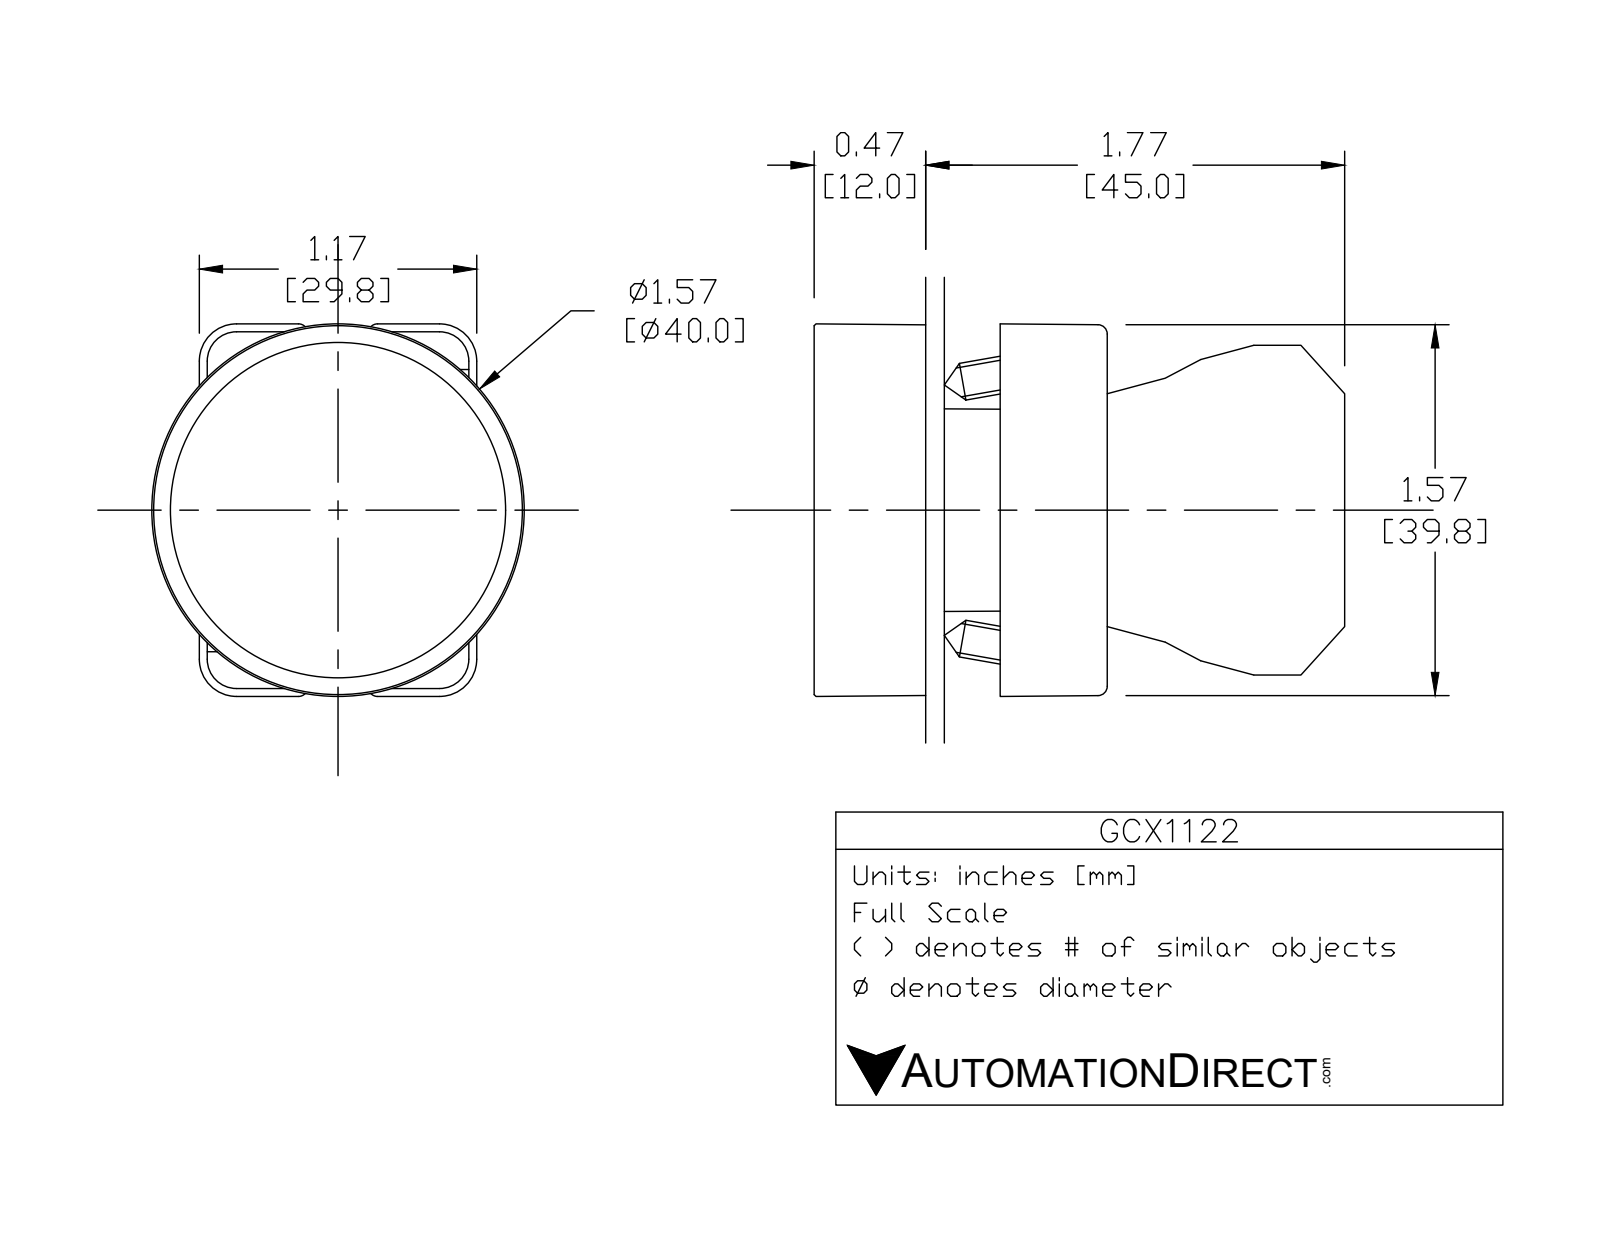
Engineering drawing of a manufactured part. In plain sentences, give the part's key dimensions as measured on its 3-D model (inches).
The part is named "GCX1122; GCX1122 OPERATOR; ecx1029; ecx1040". Its 3-D file was written by "SolidWorks 2016 (AUTOMOTIVE_DESIGN)". It is 6 solids with 381 faces: 222 planar, 132 cylindrical and 27 other. Overall it measures 2.217 by 1.581 by 1.569 inches. Its volume is 2.153 cubic inches and its surface area 32.09 square inches. Round holes: 2 of diameter 0.079, 2 of diameter 0.124, 2 of diameter 0.13, 1 of diameter 0.087, 1 of diameter 0.197, 1 of diameter 0.878, 1 of diameter 0.888, 1 of diameter 1.417. Round bosses or shafts: 2 of diameter 0.157, 1 of diameter 1.569, 1 of diameter 1.398, 1 of diameter 0.945, 1 of diameter 0.856, 1 of diameter 0.78. Partial cylindrical surfaces (rounded edges, fillets, slot ends): 24 of radius 0.059, 12 of radius 0.041, 12 of radius 0.124, 12 of radius 0.157, 4 of radius 0.039, 2 of radius 0.128, 1 of radius 0.02, 1 of radius 0.063. The main face-to-face distances are 0.472, 0.72, 1.193, 0.579, 0.7, 0.02, 0.493, 0.033, 0.031, 0.689. The hole center spacings are 0.236, 0.544, 0.472, 0.49.
